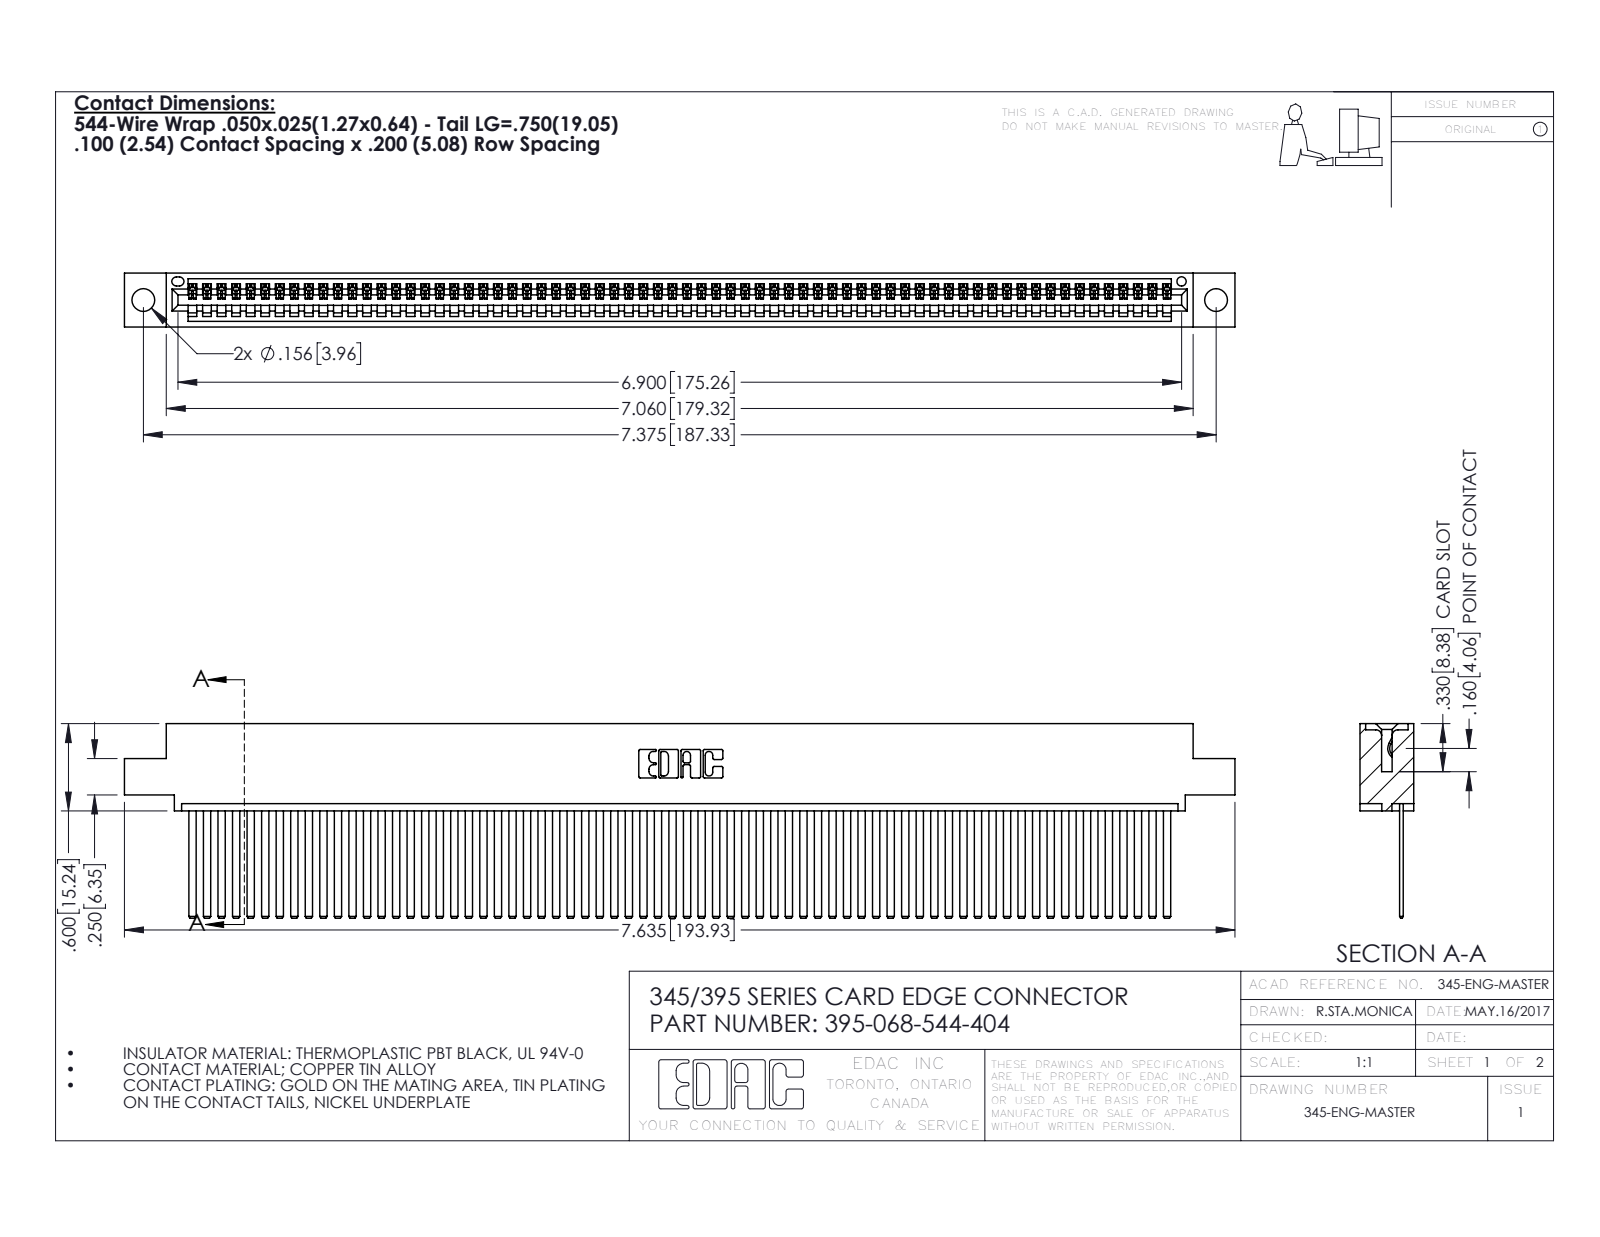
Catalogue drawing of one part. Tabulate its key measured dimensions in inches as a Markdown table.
| quantity | value |
| --- | --- |
| part name | 395-068-544-404; 345-292-001_345-293-144; 345 Part_0.110 Offset - 0.156 Dia-TH |
| STEP written by | SolidWorks 2016 (CONFIG_CONTROL_DESIGN) |
| units | inches |
| bodies | 69 solids, 3666 faces (2532 planar, 1134 cylindrical, 0 other) |
| overall size | 7.635 × 1.337 × 0.37 |
| volume | 1.175 in³ |
| surface area | 43.71 in² |
| round holes (diameter × count) | 0.156 × 2, 0.064 × 1 |
| partial cylindrical surfaces (radius × count) | 0.006 × 136, 0.01 × 22, 0.007 × 6, 0.031 × 6, 0.026 × 3, 0.031 × 2, 0.04 × 2, 0.014 × 1 |
| main face-to-face distances | 0.072, 0.298, 0.025, 0.098, 0.272, 0.37, 0.2, 0.225, 0.149, 0.072 |
| hole center spacings | 0.27, 7.139, 7.375 |
